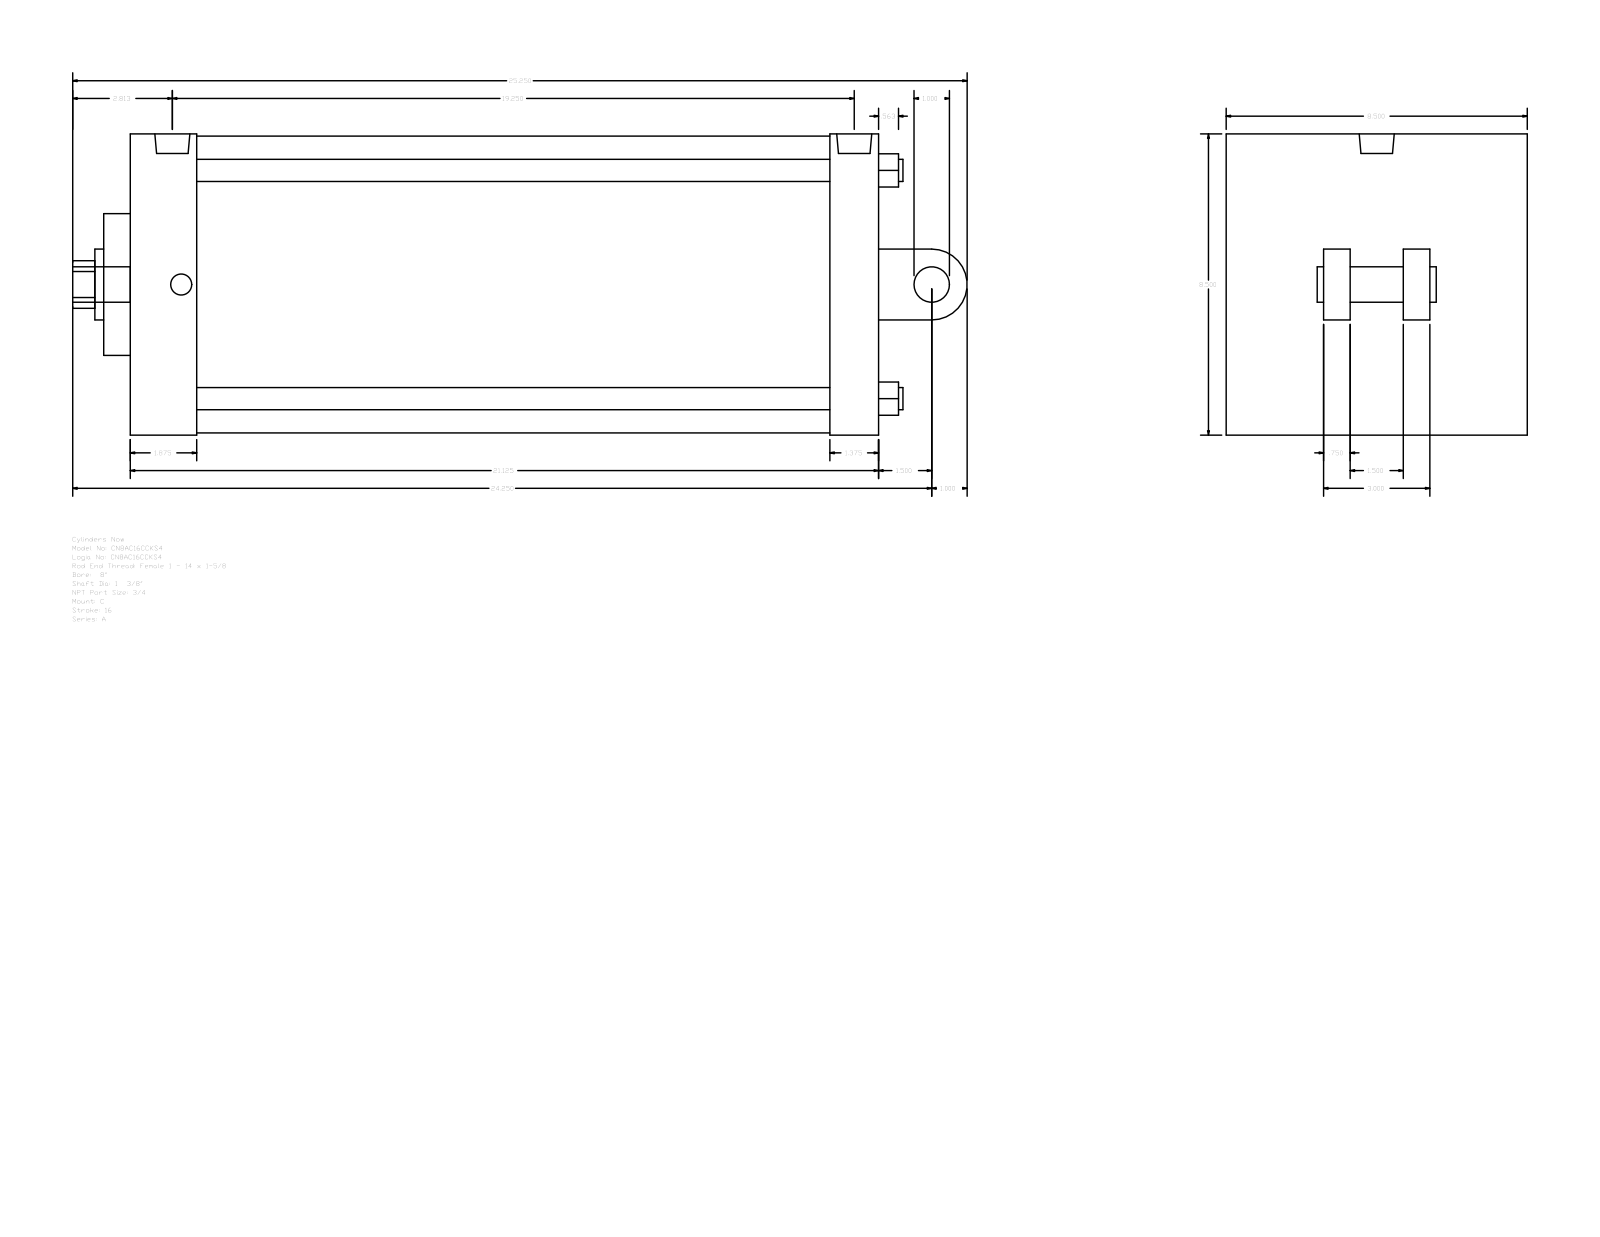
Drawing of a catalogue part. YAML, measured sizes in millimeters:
part_name: "A_C__0800_1.375"
step_written_by: "GSSL Pune (CONFIG_CONTROL_DESIGN)"
units: millimeters
bodies: {solids: 0, faces: 104, planar: 75, cylindrical: 29, other: 0}
overall_size: [641.35, 215.9, 215.9]
round_holes:
  - {diameter: 15.88, count: 4}
  - {diameter: 15.08, count: 2}
  - {diameter: 25.12, count: 1}
  - {diameter: 34.92, count: 1}
  - {diameter: 50.8, count: 1}
  - {diameter: 212.72, count: 1}
round_bosses_or_shafts:
  - {diameter: 25.4, count: 2}
  - {diameter: 15.08, count: 2}
  - {diameter: 25.12, count: 1}
partial_cylinders:
  - {radius: 17.06, count: 1}
  - {radius: 25.4, count: 1}
face_to_face_distances: [536.58, 215.9, 57.15, 47.63, 488.95, 501.65, 454.02, 34.93, 88.9, 69.85]
hole_center_spacings: [115.67, 163.58, 231.34, 6.35]
